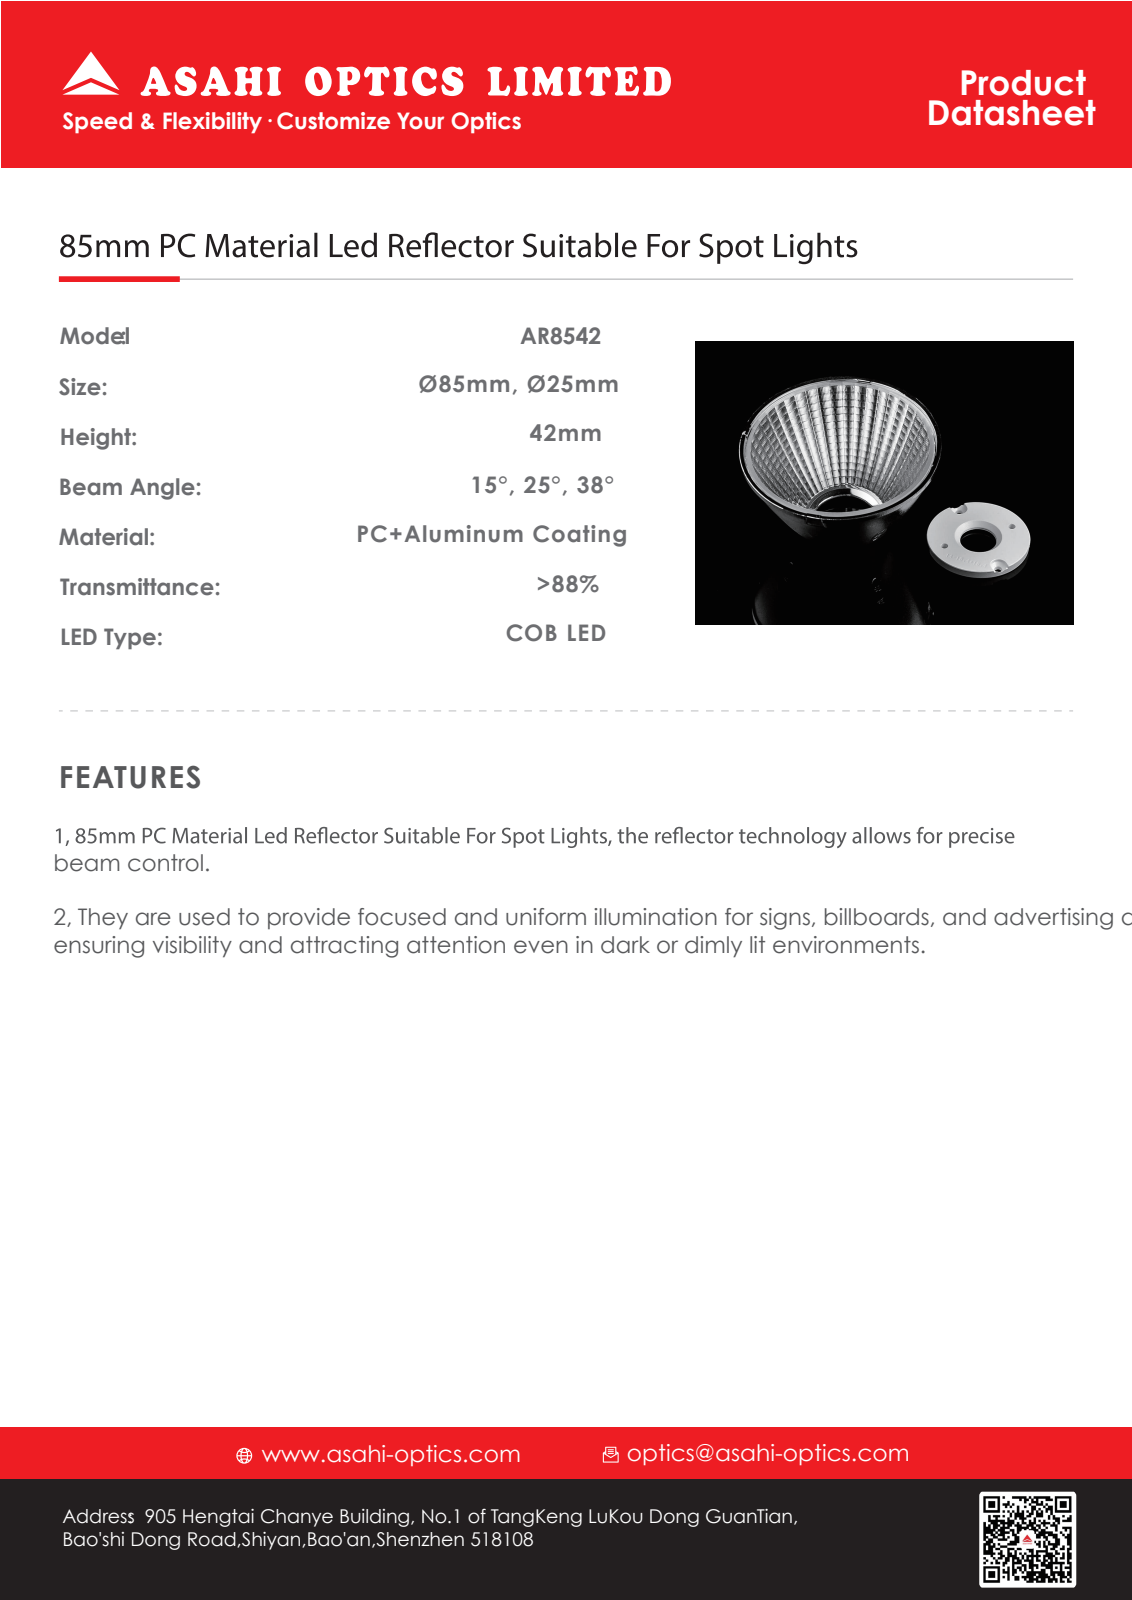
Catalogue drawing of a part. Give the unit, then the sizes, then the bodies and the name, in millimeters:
Units: millimetres
Overall size (bounding box): 85 × 85 × 43.7
Round holes (diameter × count): ⌀25 ×1, ⌀81.5 ×1
Round bosses / shafts (diameter × count): ⌀2.7 ×2, ⌀85 ×1
Partial cylindrical surfaces — rounded edges, fillets, slot ends (radius × count): R40.25 ×1
Main face-to-face distances: 1, 39, 41, 42, 38, 3, 40, 2, 1.7, 2.7
Volume: 14 112 mm³ · Surface area: 21 333 mm²
Bodies: 1 solid, 78 faces (30 planar, 18 cylindrical, 30 other)
Part name (STEP PRODUCT): SL-085B-3D-V1
STEP written by: SolidWorks 2014 (CONFIG_CONTROL_DESIGN)
